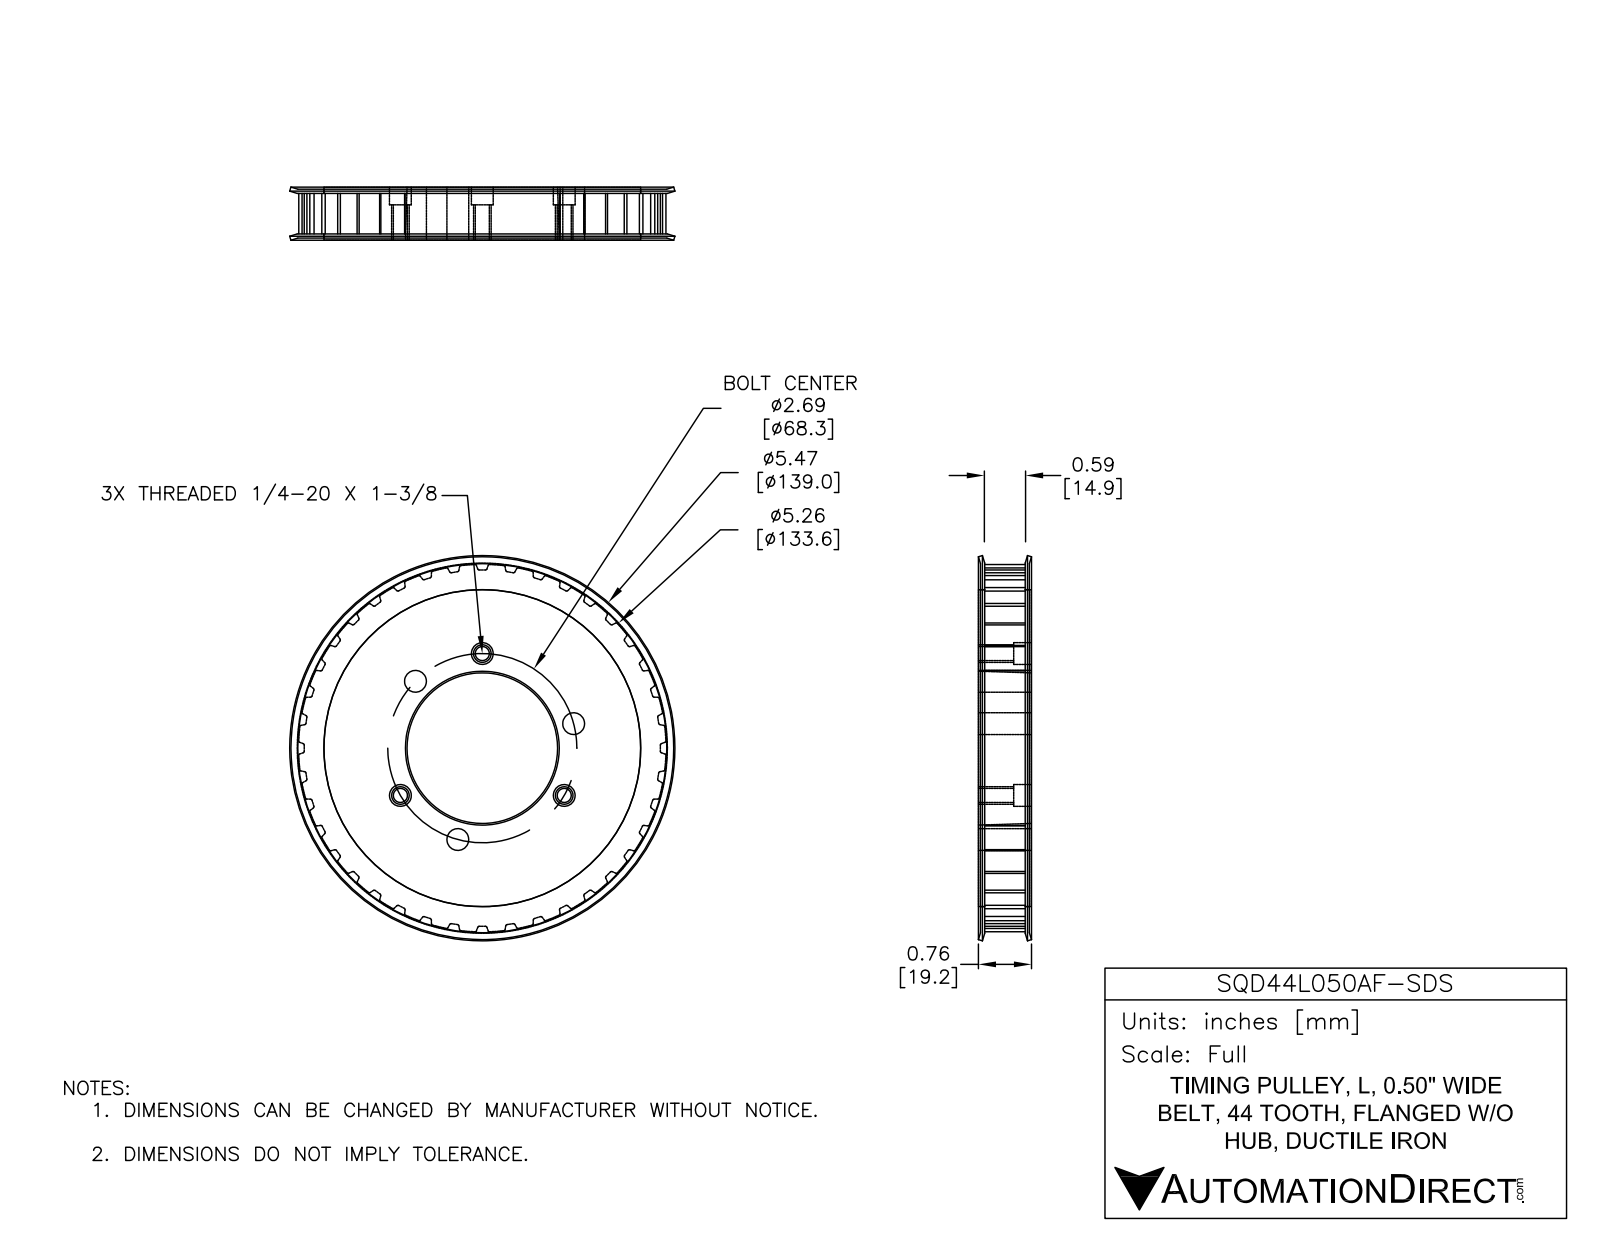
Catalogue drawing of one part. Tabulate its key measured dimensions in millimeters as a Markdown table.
| quantity | value |
| --- | --- |
| part name | SQD44L050AF-SDS |
| STEP written by | SolidWorks 2018 (AUTOMOTIVE_DESIGN) |
| units | millimeters |
| bodies | 4 solids, 401 faces (131 planar, 256 cylindrical, 14 other) |
| overall size | 139 × 139 × 19.2 |
| volume | 208 100 mm³ |
| surface area | 69 100 mm² |
| round holes (diameter × count) | 7.9 × 6, 5.1 × 3, 114.3 × 1, 114.4 × 1 |
| partial cylindrical surfaces (radius × count) | 0.4 × 80, 0.5 × 80, 66.3 × 1 |
| main face-to-face distances | 19.1, 0.7, 18.3, 2.2, 16.8, 16.8, 14.6, 2.2, 1.5, 16.1 |
| hole center spacings | 59.1, 34.1, 26.1, 34.1, 41.6, 59.1, 67.7, 26.1 |
